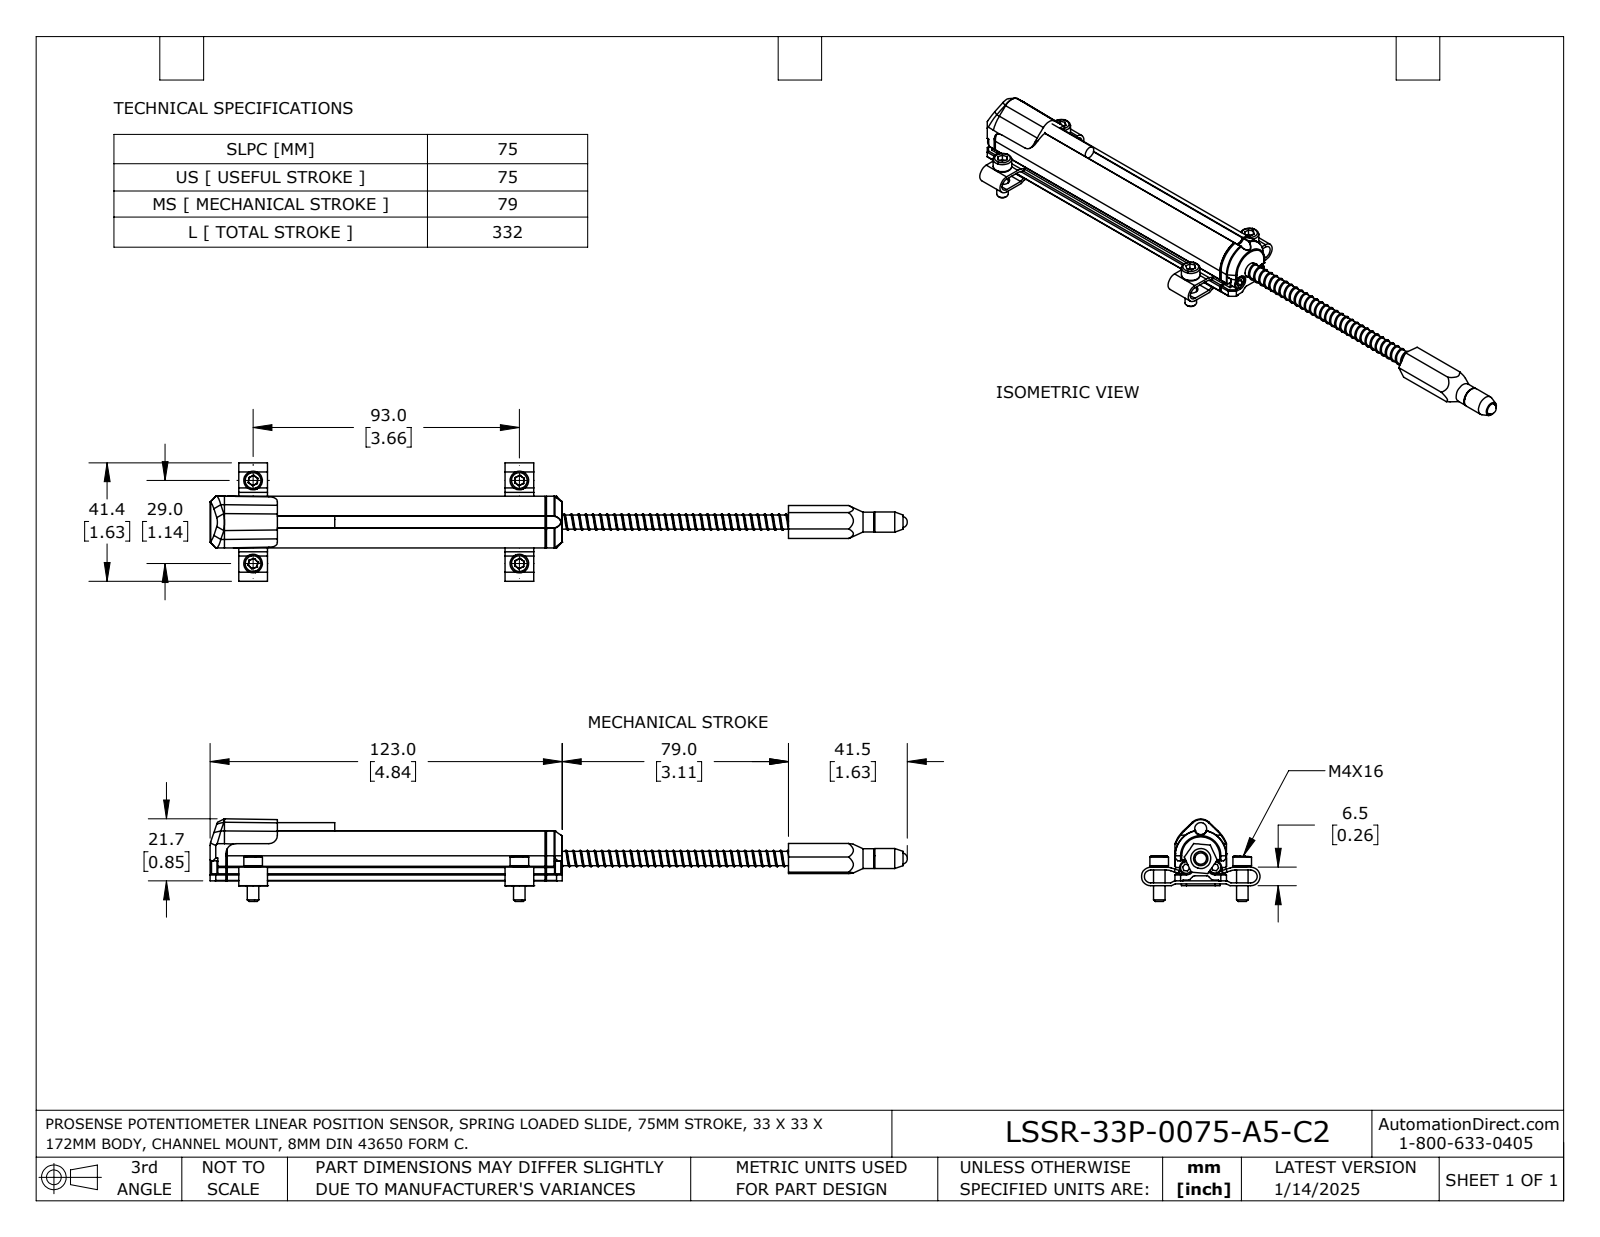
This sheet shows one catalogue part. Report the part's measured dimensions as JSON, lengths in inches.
{"part_name": "LSSR-33P-0075-A5-C2", "step_written_by": "SolidWorks 2023 (AUTOMOTIVE_DESIGN)", "units": "inches", "bodies": {"solids": 22, "faces": 611, "planar": 374, "cylindrical": 173, "other": 64}, "overall_size": [9.587, 1.63, 1.136], "volume_in3": 2.442, "surface_area_in2": 37.4, "round_holes": [[0.177, 4], [0.197, 4], [0.102, 2], [0.104, 2], [0.157, 1], [0.213, 1], [0.27, 1], [0.272, 1], [0.335, 1]], "round_bosses_or_shafts": [[0.256, 4], [0.157, 4], [0.181, 3], [0.113, 2], [0.113, 2], [0.059, 2], [0.276, 1], [0.197, 1]], "partial_cylinders_radius": [[0.008, 8], [0.059, 8], [0.004, 6], [0.02, 6], [0.012, 4], [0.049, 4], [0.069, 4], [0.089, 4]], "face_to_face_distances": [0.028, 0.039, 0.02, 4.39, 0.709, 0.394, 0.138, 0.098, 0.071, 0.063], "hole_center_spacings": [0.231, 1.142, 3.661, 3.835, 0.394]}
